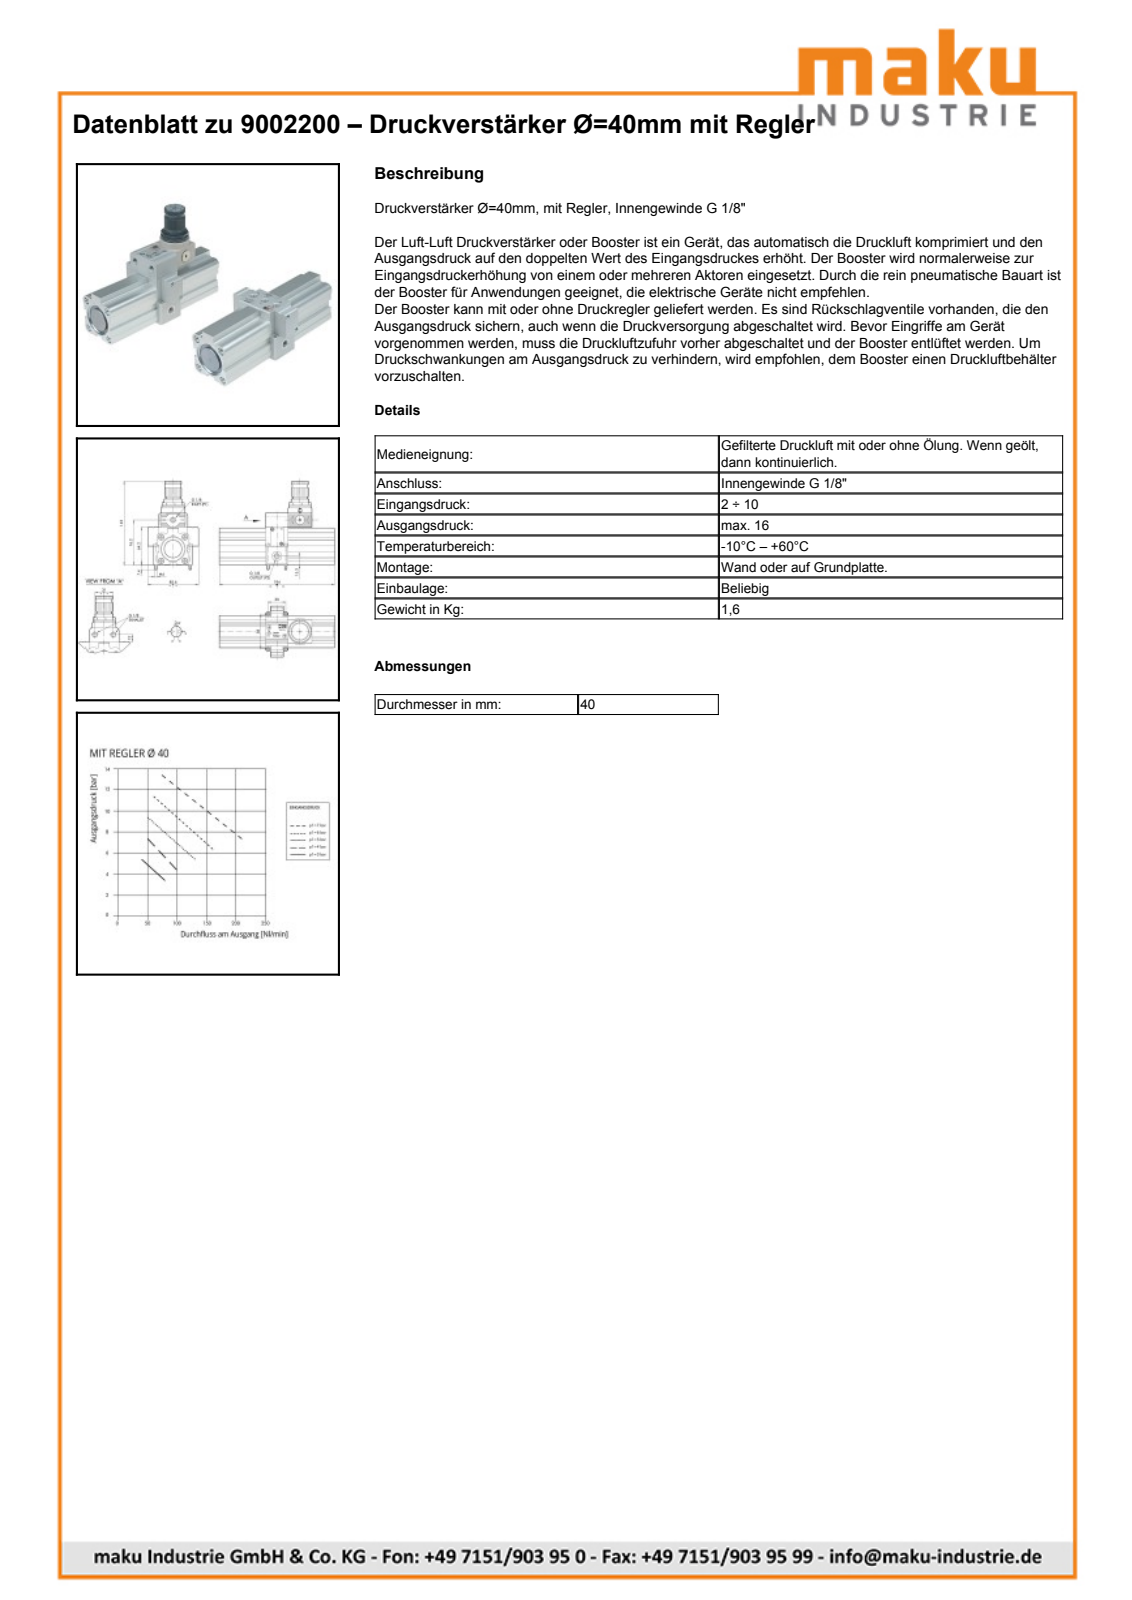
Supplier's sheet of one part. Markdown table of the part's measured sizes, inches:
| quantity | value |
| --- | --- |
| part name | 9002200; 9002100; 40-regulator-unit; 5107001-BD (+2 more) |
| STEP written by | PARTsolutions (AUTOMOTIVE_DESIGN) |
| units | inches |
| bodies | 6 solids, 549 faces (392 planar, 122 cylindrical, 35 other) |
| overall size | 7.638 × 5.886 × 3.37 |
| volume | 44.15 in³ |
| surface area | 142.7 in² |
| round holes (diameter × count) | 0.337 × 7, 0.236 × 4, 0.394 × 4, 0.128 × 2, 0.157 × 2, 0.177 × 2, 0.295 × 2, 0.61 × 1, 1.634 × 1 |
| round bosses / shafts (diameter × count) | 0.236 × 6, 0.157 × 6, 1.181 × 2, 0.276 × 2, 1.571 × 1, 1.496 × 1, 1.48 × 1, 1.102 × 1 |
| partial cylindrical surfaces (radius × count) | 0.008 × 12, 0.004 × 8, 0.276 × 4, 0.098 × 2, 0.118 × 2, 0.236 × 2, 0.472 × 1 |
| main face-to-face distances | 0.118, 0.033, 0.055, 0.152, 0.315, 1.961, 2.472, 2.528, 1.331, 1.26 |
| hole center spacings | 1.12, 0.587, 0.591, 0.61, 0.663, 0.709, 0.969, 1.12 |
